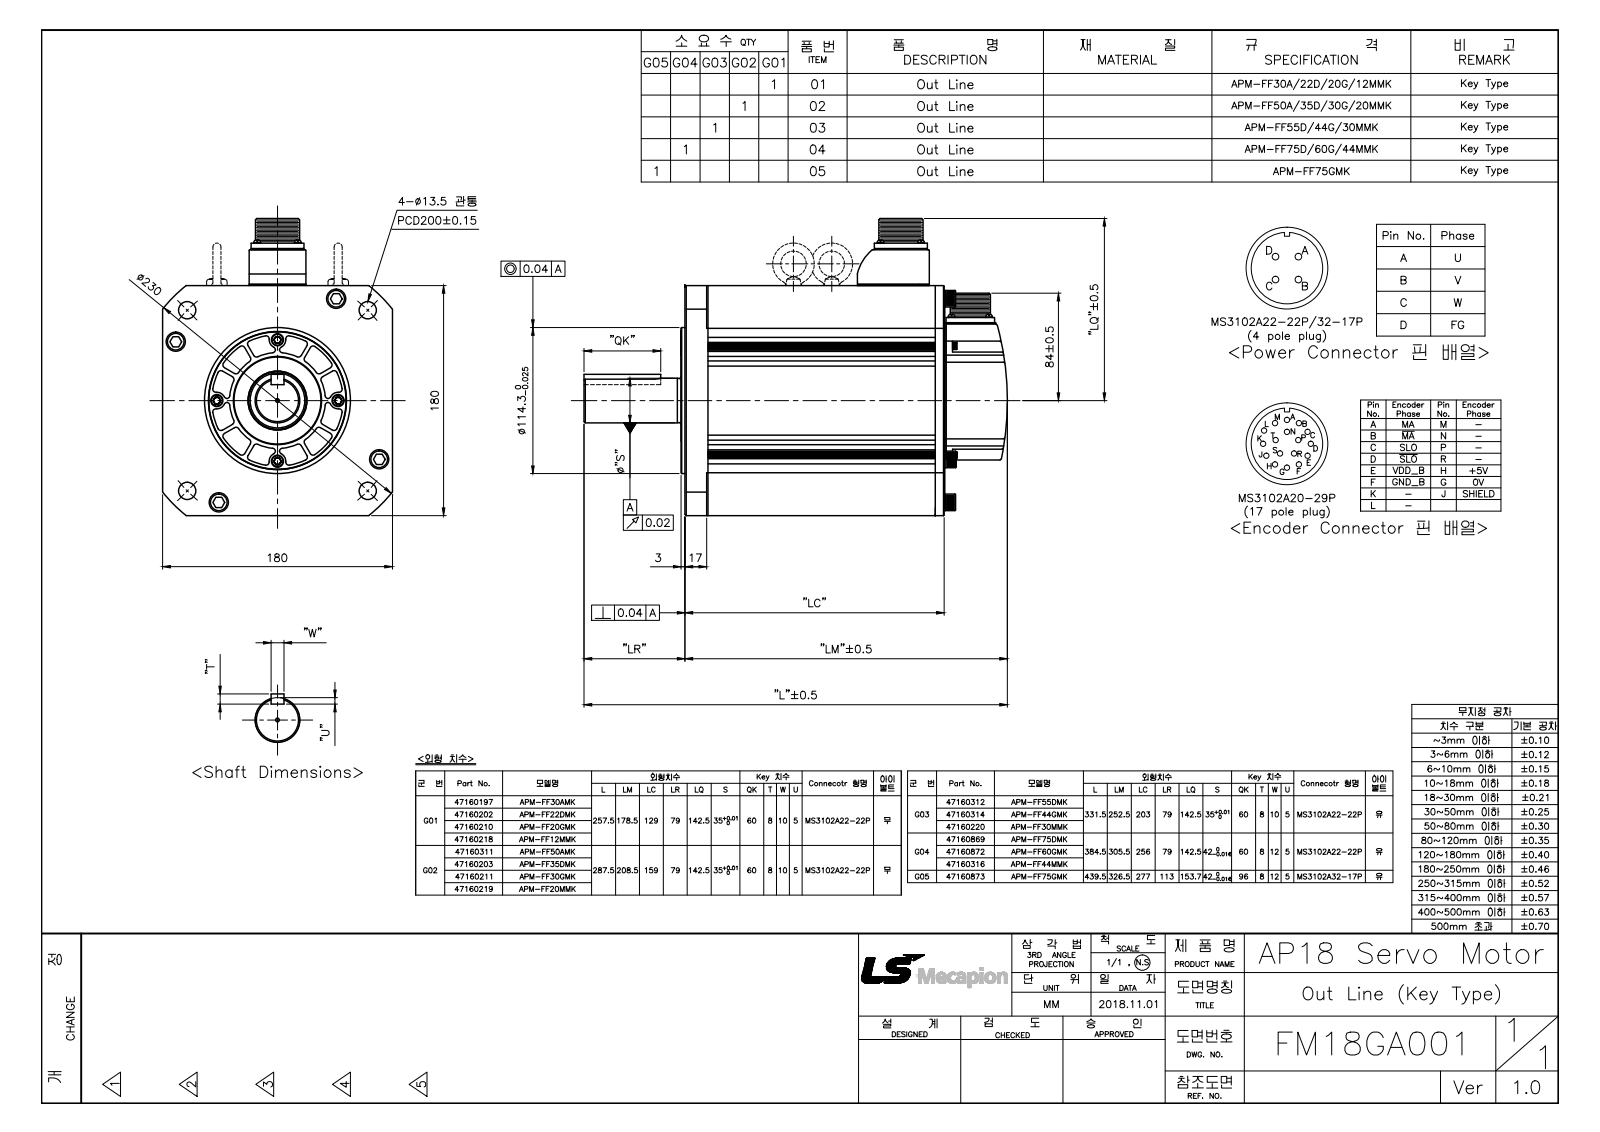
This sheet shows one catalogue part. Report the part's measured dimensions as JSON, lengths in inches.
{"part_name": "FM18GA001G03_Out Line(APM-FF55D_K,FF44G_K,FF30M_K)", "step_written_by": "SolidWorks 2011 (AUTOMOTIVE_DESIGN)", "units": "inches", "bodies": {"solids": 57, "faces": 2370, "planar": 798, "cylindrical": 882, "other": 690}, "overall_size": [13.051, 9.154, 7.087], "volume_in3": 380.4, "surface_area_in2": 798.4, "round_holes": [[0.118, 13], [0.098, 9], [0.12, 8], [0.236, 8], [0.374, 8], [0.268, 6], [0.138, 4], [0.142, 4], [0.146, 4], [0.197, 4], [0.354, 4], [0.362, 4]], "round_bosses_or_shafts": [[0.063, 17], [0.213, 8], [0.52, 4], [0.512, 4], [0.335, 4], [0.315, 4], [0.217, 4], [0.118, 4]], "partial_cylinders_radius": [[0.02, 124], [0.098, 56], [0.157, 24], [0.079, 17], [0.039, 14], [0.177, 12], [0.256, 4], [0.012, 2]], "face_to_face_distances": [7.008, 0.039, 7.087, 0.709, 0.315, 0.394, 0.276, 0.295, 1.319, 5.768], "hole_center_spacings": [1.282, 2.93, 5.423, 0.042, 0.819, 0.885, 0.927, 1.035]}
